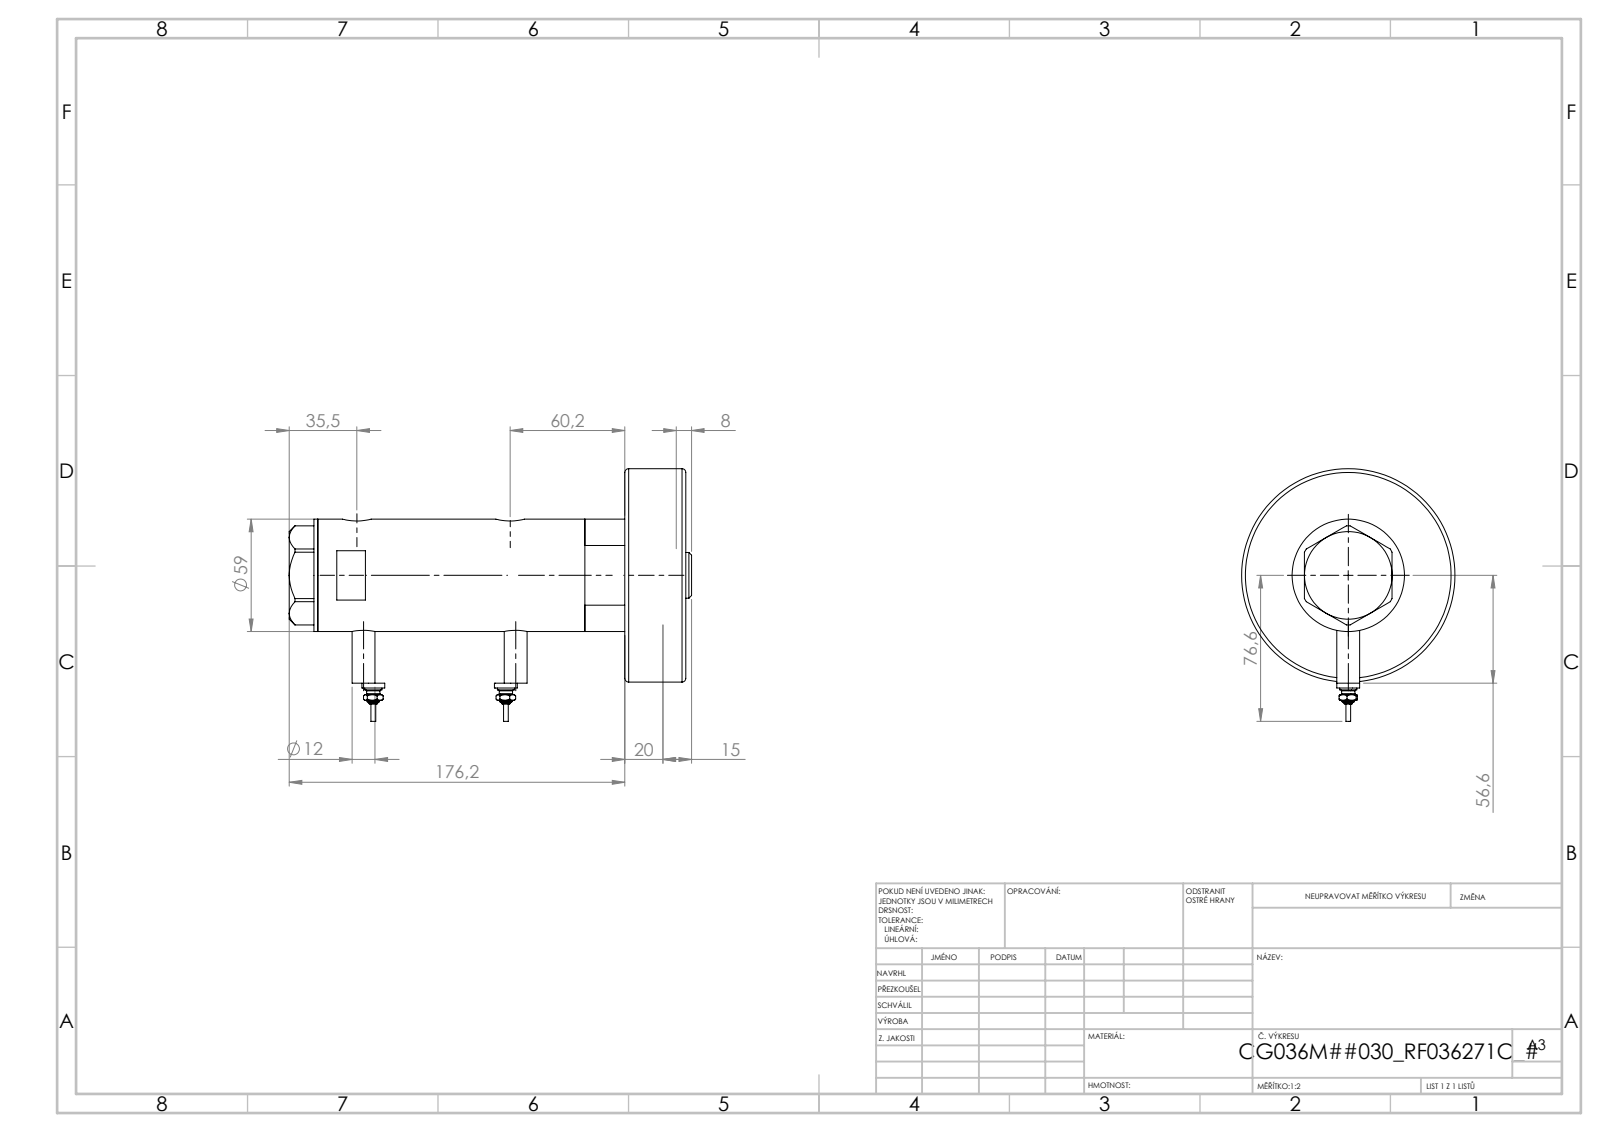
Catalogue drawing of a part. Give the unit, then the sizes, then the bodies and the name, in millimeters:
Units: millimetres
Overall size (bounding box): 193.42 × 117.8 × 112
Round holes (diameter × count): ⌀5 ×2, ⌀9.73 ×2, ⌀12.5 ×2, ⌀15 ×2, ⌀8.5 ×1, ⌀25 ×1, ⌀26.5 ×1, ⌀36 ×1, ⌀40 ×1, ⌀48 ×1, ⌀52 ×1
Round bosses / shafts (diameter × count): ⌀12 ×3, ⌀9 ×2, ⌀7 ×2, ⌀4.34 ×2, ⌀2.4 ×2, ⌀112 ×1, ⌀59 ×1, ⌀46 ×1
Main face-to-face distances: 32, 140.84, 172.84, 87.34, 53.5, 85.5, 23.5, 63.84, 117.34, 149.34
Hole centre spacings: 2.9, 3.5, 62.15, 65.05, 65.65, 68.55, 2.89, 2.91
Volume: 696 967 mm³ · Surface area: 126 712 mm²
Bodies: 7 solids, 242 faces (83 planar, 81 cylindrical, 78 other)
Part name (STEP PRODUCT): V270CG_BACK; V270CG_VC; V270CG_MIDDLE; V270CG_FRONT (+2 more)
STEP written by: SolidWorks 2019 (CONFIG_CONTROL_DESIGN)
